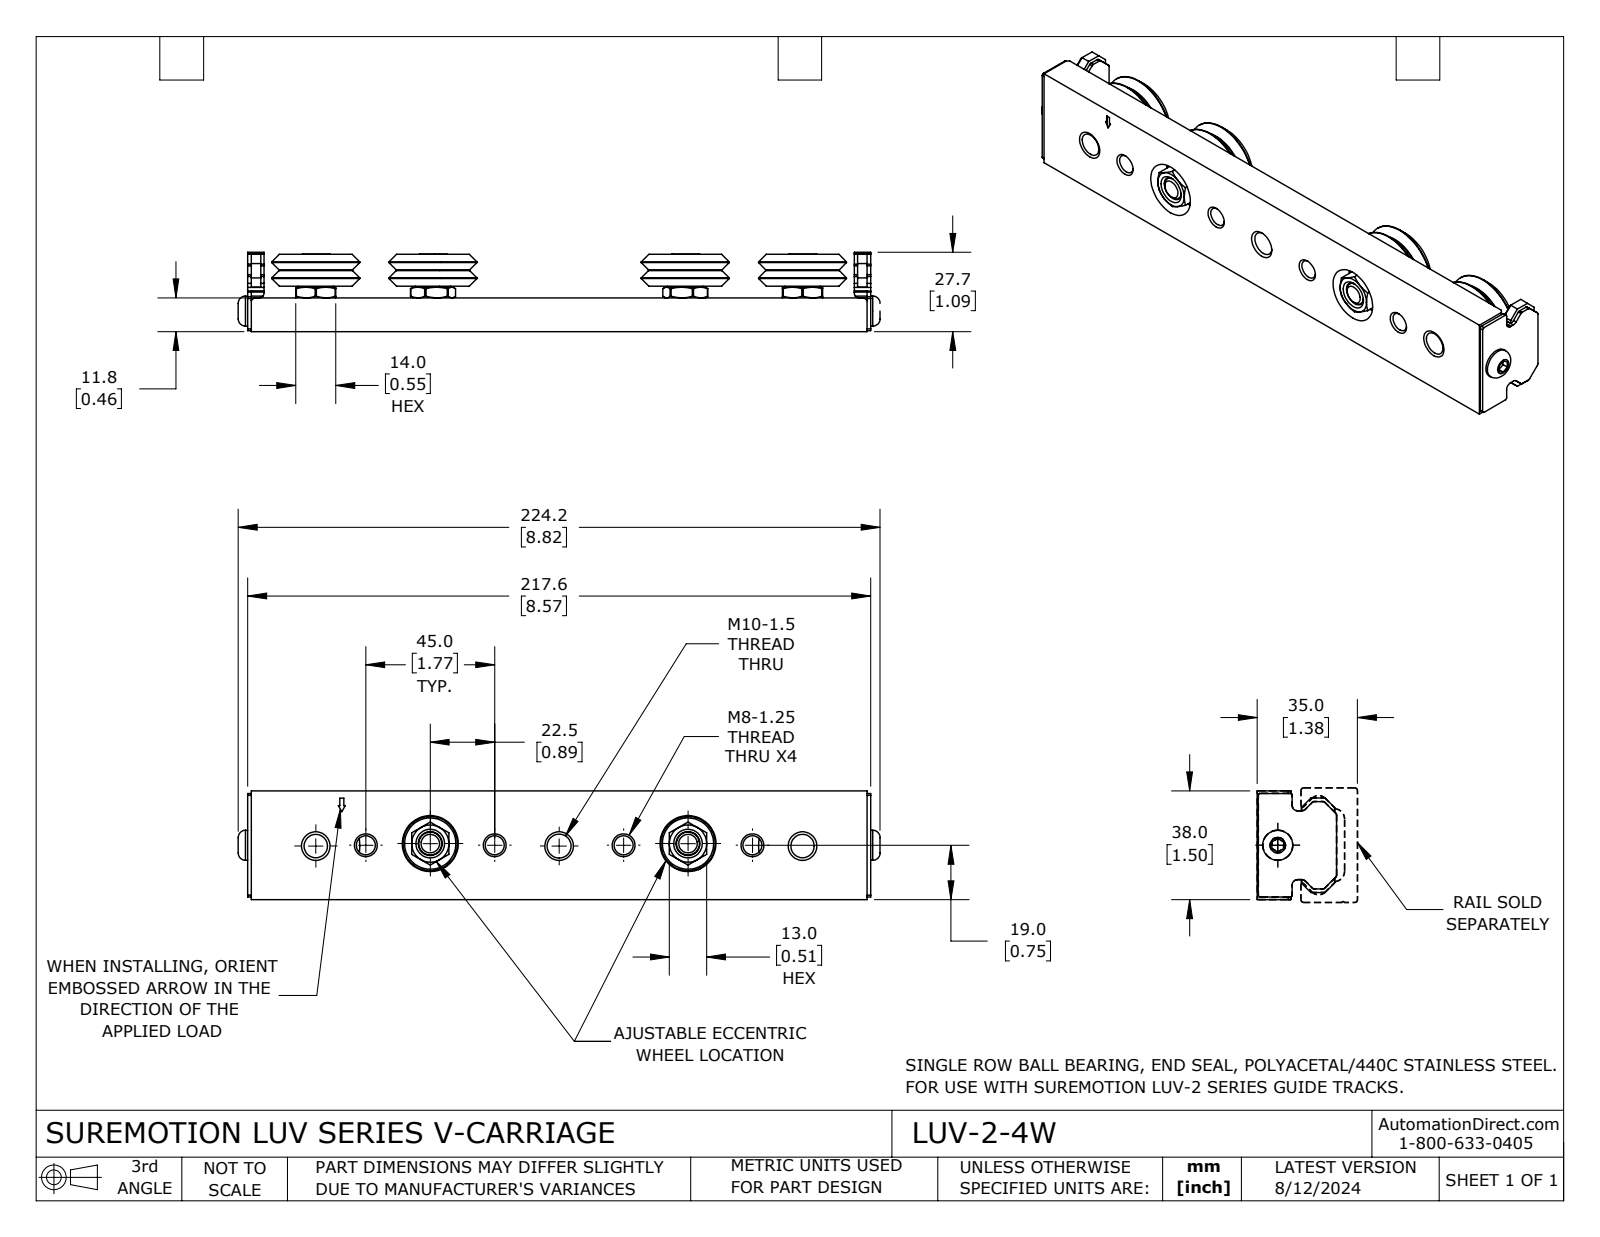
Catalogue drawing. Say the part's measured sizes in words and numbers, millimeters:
The part is named "LUV-2-4W". Its 3-D file was written by "SolidWorks 2023 (CONFIG_CONTROL_DESIGN)". It is 9 solids with 860 faces: 274 planar, 250 cylindrical and 336 other. Overall it measures 224.15 by 38 by 27.69 millimeters. Its volume is 127 962 cubic millimeters and its surface area 46 912 square millimeters. Round holes: 5 of diameter 8.38, 4 of diameter 6.65, 4 of diameter 9.53, 4 of diameter 20.12, 4 of diameter 20.35, 2 of diameter 9.59, 2 of diameter 19.56, 1 of diameter 4.92, 1 of diameter 4.92. Round bosses or shafts: 4 of diameter 30.73, 4 of diameter 14.83, 4 of diameter 9.51, 2 of diameter 14.61, 2 of diameter 14.6, 2 of diameter 10, 2 of diameter 9.52, 2 of diameter 8. Partial cylindrical surfaces (rounded edges, fillets, slot ends): 12 of radius 0.64, 6 of radius 0.38, 6 of radius 0.84, 4 of radius 1.98, 4 of radius 7.95, 2 of radius 1.78. The main face-to-face distances are 11.79, 38, 1.27, 216.29, 10.88, 15.18, 26.97, 11.11, 4.07, 15.86. The hole center spacings are 22.51, 45.01, 90.02, 0.97, 22.52, 44.07, 45.02, 67.51.
